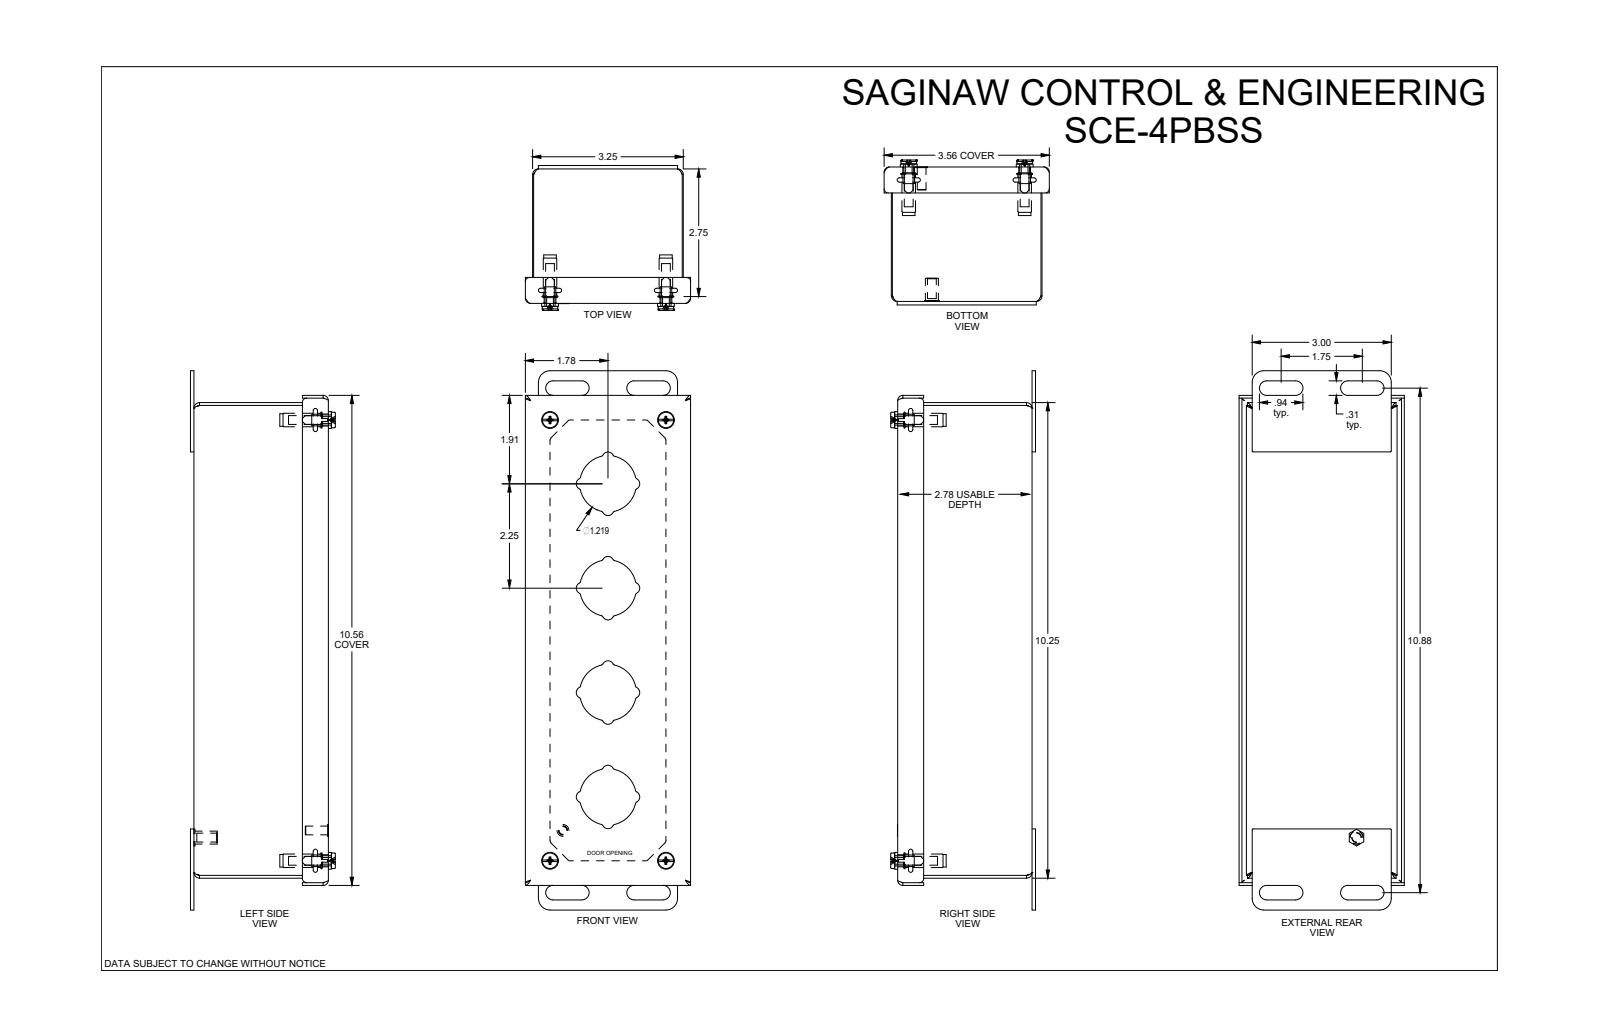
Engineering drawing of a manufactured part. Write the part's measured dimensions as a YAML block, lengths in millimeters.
part_name: "SCE-4PB"
step_written_by: "SolidWorks 2021 (AUTOMOTIVE_DESIGN)"
units: millimeters
bodies: {solids: 14, faces: 466, planar: 159, cylindrical: 166, other: 141}
overall_size: [295.3, 90.5, 79.3]
volume: 178800
surface_area: 233500
round_holes:
  - {diameter: 5.6, count: 4}
  - {diameter: 6.8, count: 4}
  - {diameter: 8.1, count: 4}
round_bosses_or_shafts:
  - {diameter: 4.8, count: 5}
  - {diameter: 9.2, count: 4}
  - {diameter: 8.5, count: 4}
  - {diameter: 6.6, count: 4}
  - {diameter: 3.7, count: 4}
  - {diameter: 6.5, count: 1}
partial_cylinders:
  - {radius: 1, count: 32}
  - {radius: 1.5, count: 28}
  - {radius: 3.2, count: 16}
  - {radius: 0.4, count: 8}
  - {radius: 2.9, count: 8}
  - {radius: 4, count: 8}
  - {radius: 6.2, count: 8}
  - {radius: 0.5, count: 4}
face_to_face_distances: [1.5, 72.1, 81, 70.6, 73.6, 82.6, 79.5, 258.8, 68.3, 3.8]
hole_center_spacings: [63.5, 241.3, 249.5, 241.3, 241.3, 249.5, 249.5]
